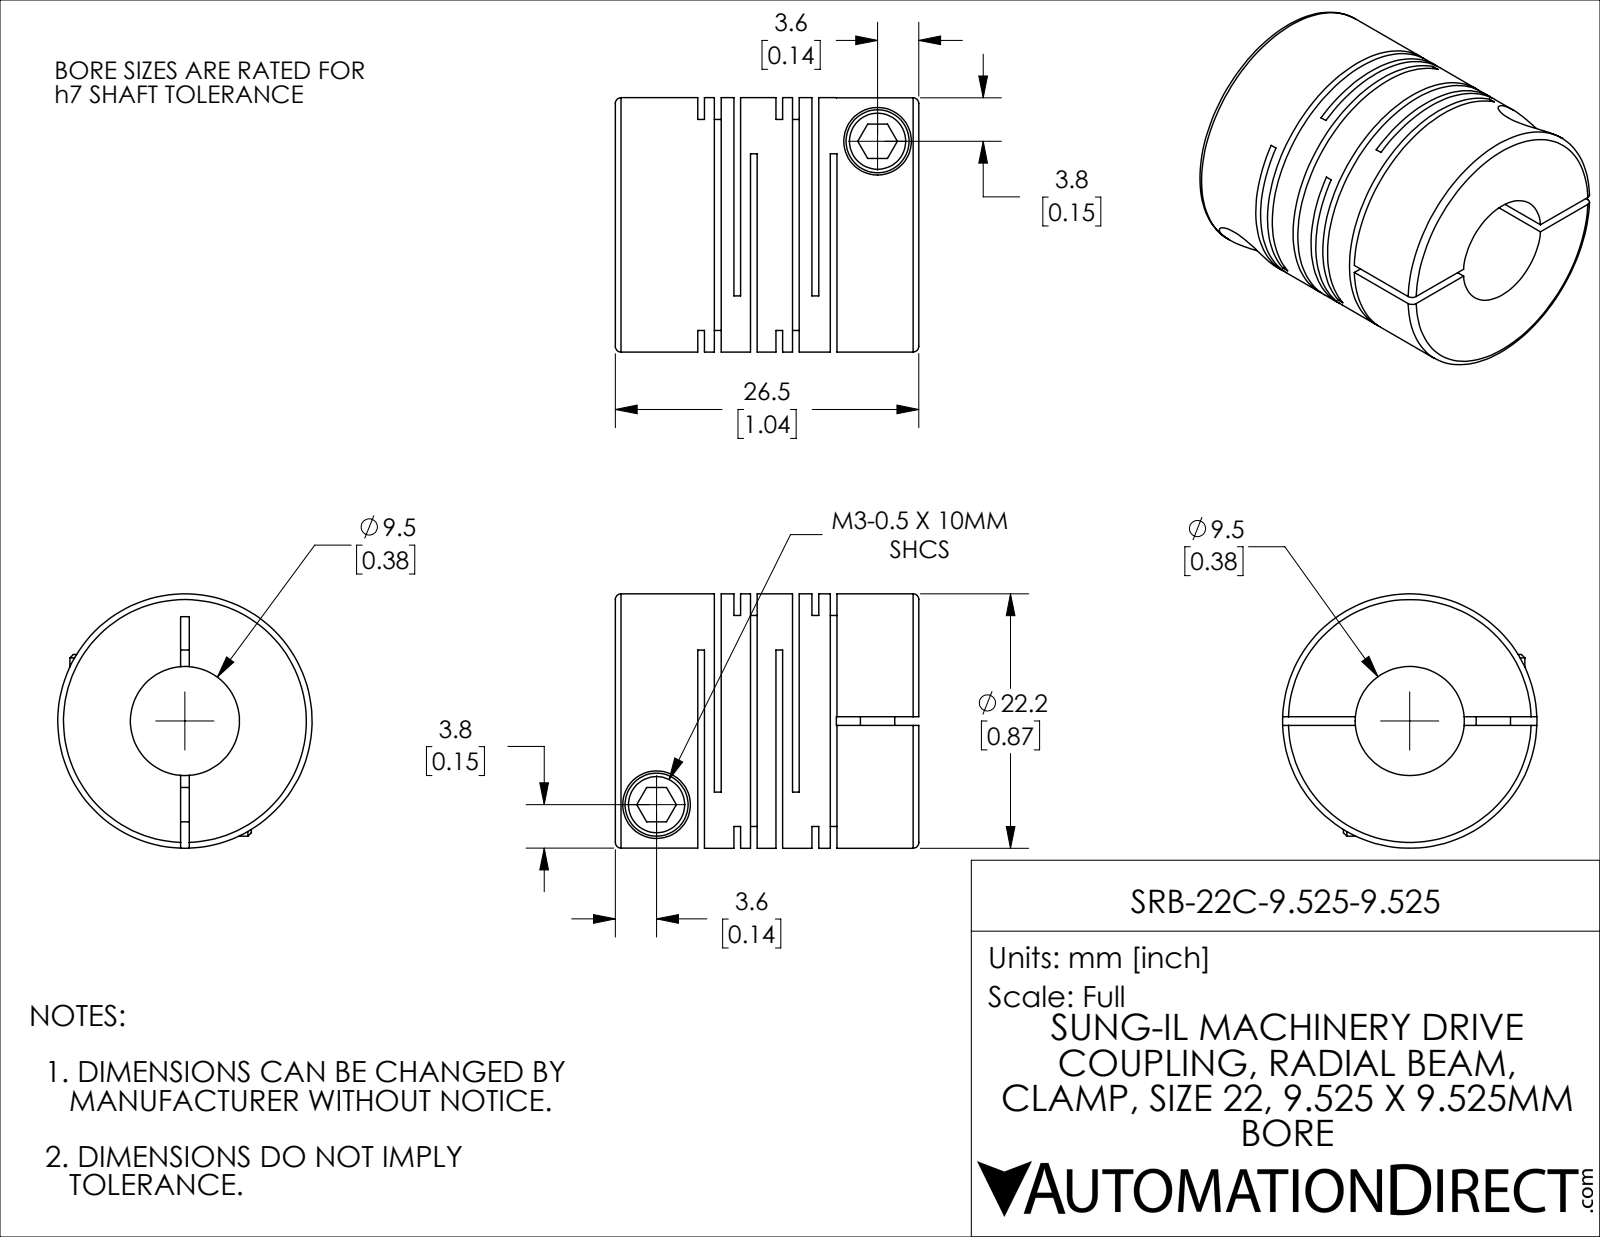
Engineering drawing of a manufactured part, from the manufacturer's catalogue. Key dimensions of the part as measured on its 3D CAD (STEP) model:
Part name (STEP PRODUCT): SRB-22C-9.525-9.525
STEP written by: SolidWorks 2021 (CONFIG_CONTROL_DESIGN)
Units: millimetres
Bodies: 1 solid, 115 faces (60 planar, 42 cylindrical, 13 other)
Overall size (bounding box): 26.5 × 22.2 × 22.2
Volume: 6 870 mm³ · Surface area: 7 547 mm²
Round holes (diameter × count): ⌀3 ×2, ⌀5.9 ×2, ⌀9.53 ×1
Round bosses / shafts (diameter × count): ⌀5.5 ×2, ⌀22.2 ×1
Main face-to-face distances: 0.59, 6.82, 1.45, 3.15, 5.37, 3.67, 1.7, 6.23, 2.56, 0.86
